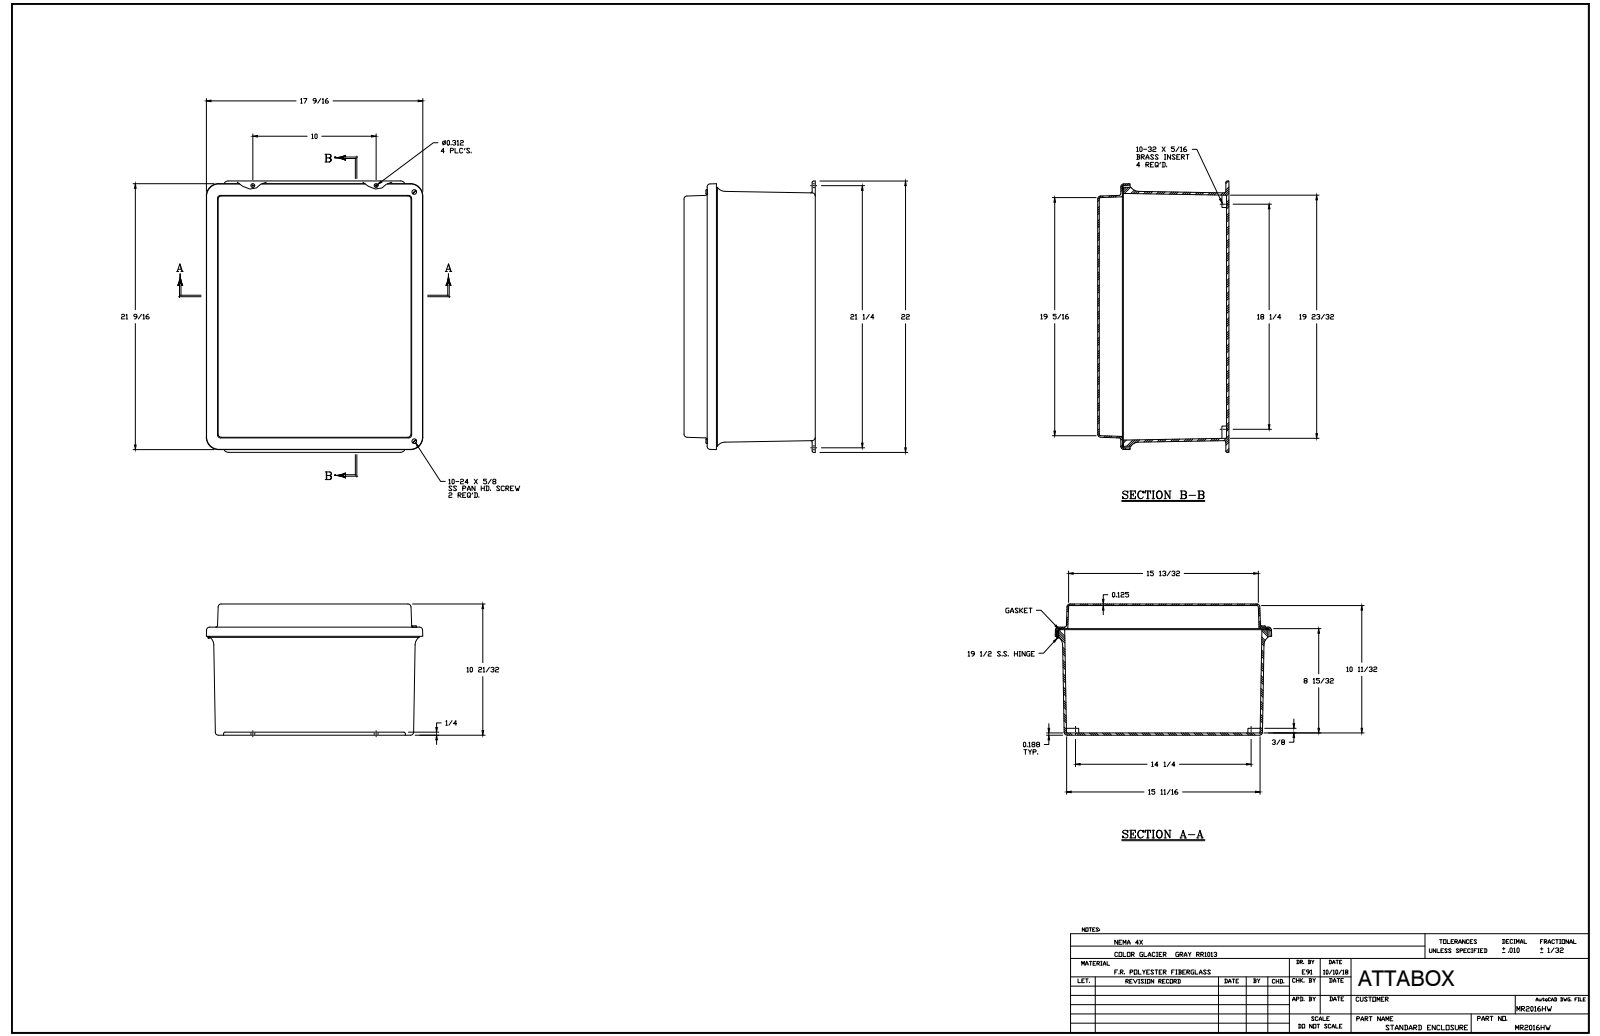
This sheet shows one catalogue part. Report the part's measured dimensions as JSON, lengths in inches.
{"part_name": "MR2016HW", "step_written_by": "SolidWorks 2018 (AUTOMOTIVE_DESIGN)", "units": "inches", "bodies": {"solids": 26, "faces": 1027, "planar": 403, "cylindrical": 399, "other": 225}, "overall_size": [22, 17.588, 10.642], "volume_in3": 270.7, "surface_area_in2": 3159, "round_holes": [[0.131, 12], [0.14, 12], [0.152, 5], [0.156, 4], [0.218, 4], [0.145, 2], [0.085, 1]], "round_bosses_or_shafts": [[0.25, 12], [0.27, 6], [0.125, 6], [0.125, 6], [0.19, 2], [0.156, 2], [0.155, 1], [0.155, 1]], "partial_cylinders_radius": [[0.125, 22], [0.031, 20], [0.25, 12], [0.2, 5], [0.062, 4], [0.375, 4], [0.75, 4]], "face_to_face_distances": [0.187, 0.125, 0.188, 10.517, 10.329, 10.642, 10.454, 2, 8.642, 8.454], "hole_center_spacings": [3.75, 7.5, 0.25, 3.5, 4, 7.25, 7.75, 11]}
